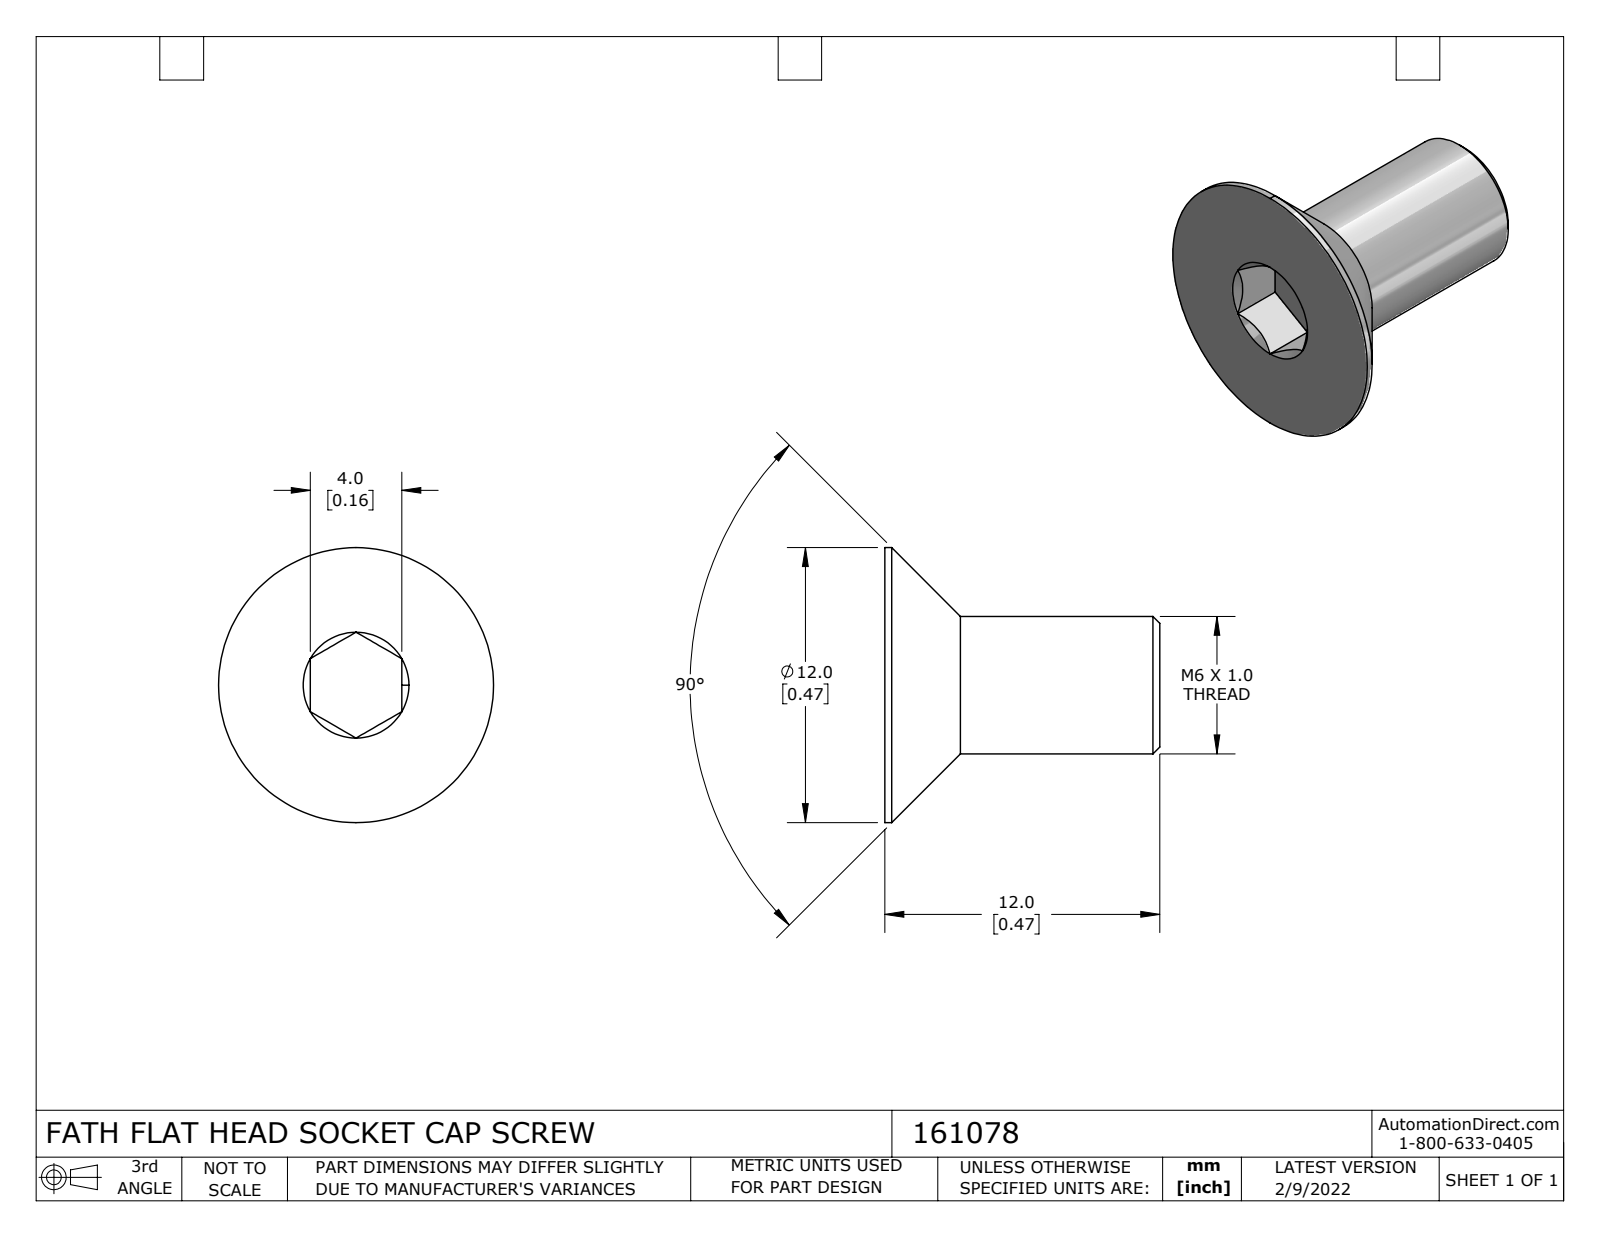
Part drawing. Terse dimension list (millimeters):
name: 161078
written by: SolidWorks 2021 (CONFIG_CONTROL_DESIGN)
unit: mm
bodies: 1 solid, 24 faces (9 planar, 4 cylindrical, 11 other)
size: 12 × 12 × 12
volume: 445 mm³; area: 464 mm²
bosses: 1× ⌀12, 1× ⌀6
face distances: 12, 4, 9.69, 2.31
